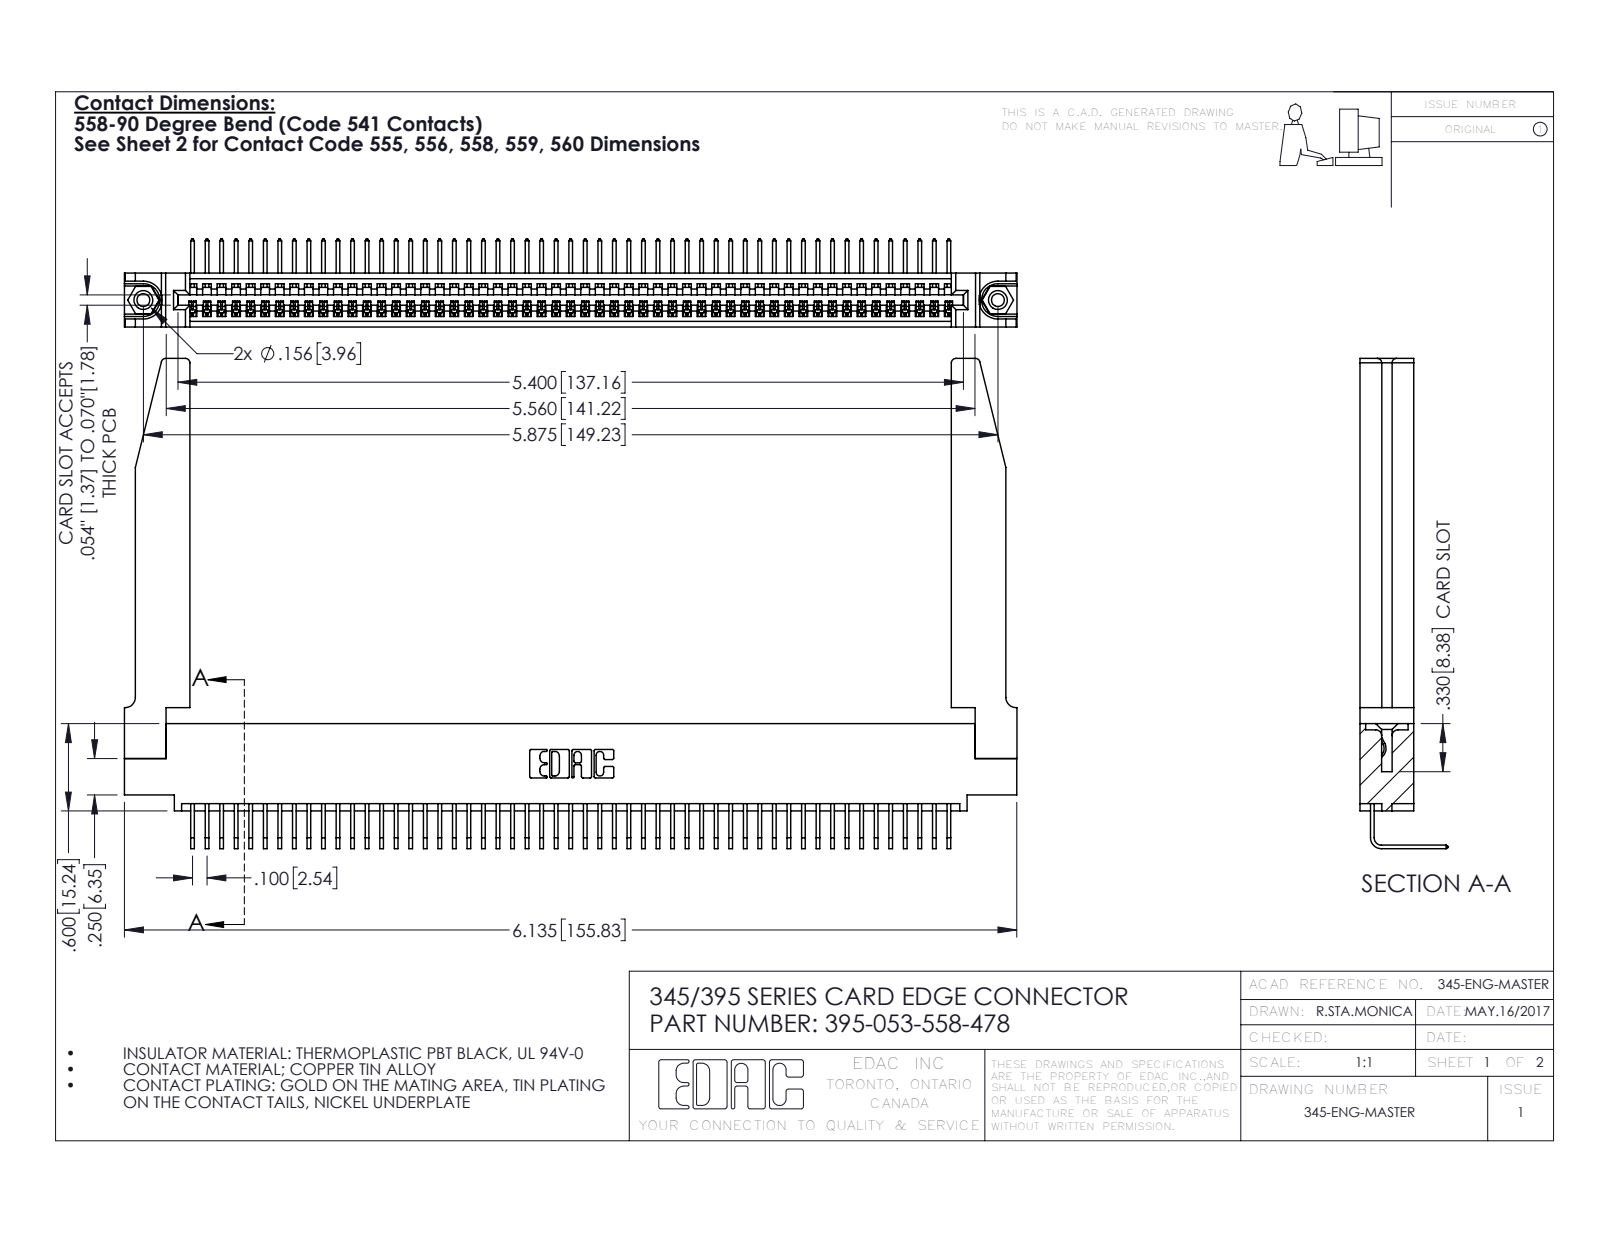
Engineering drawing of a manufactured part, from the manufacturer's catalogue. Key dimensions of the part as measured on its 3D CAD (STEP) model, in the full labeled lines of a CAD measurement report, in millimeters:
Part name (STEP PRODUCT): 345-292-001_558 Tail - 2; 345-220-078_345-220-078; 395-053-558-478; 345-250-001_345-250-001-102 (+1 more)
STEP written by: SolidWorks 2016 (CONFIG_CONTROL_DESIGN)
Units: millimetres
Bodies: 58 solids, 3544 faces (2452 planar, 1040 cylindrical, 52 other)
Overall size (bounding box): 155.9 × 85.6 × 15.4
Volume: 22 760 mm³ · Surface area: 28 050 mm²
Round holes (diameter × count): ⌀2.3 ×2, ⌀3.2 ×2, ⌀4 ×2, ⌀1.6 ×1
Round bosses / shafts (diameter × count): ⌀3.9 ×2
Partial cylindrical surfaces — rounded edges, fillets, slot ends (radius × count): R0.2 ×106, R0.3 ×22, R0.8 ×8, R0.2 ×6, R0.8 ×6, R0.7 ×3, R0.8 ×2, R1 ×2
Main face-to-face distances: 9.4, 1.8, 7.6, 5.1, 2.5, 6.9, 0.6, 5.7, 3.8, 3.8
Hole centre spacings: 6.9, 143.2, 149.2
